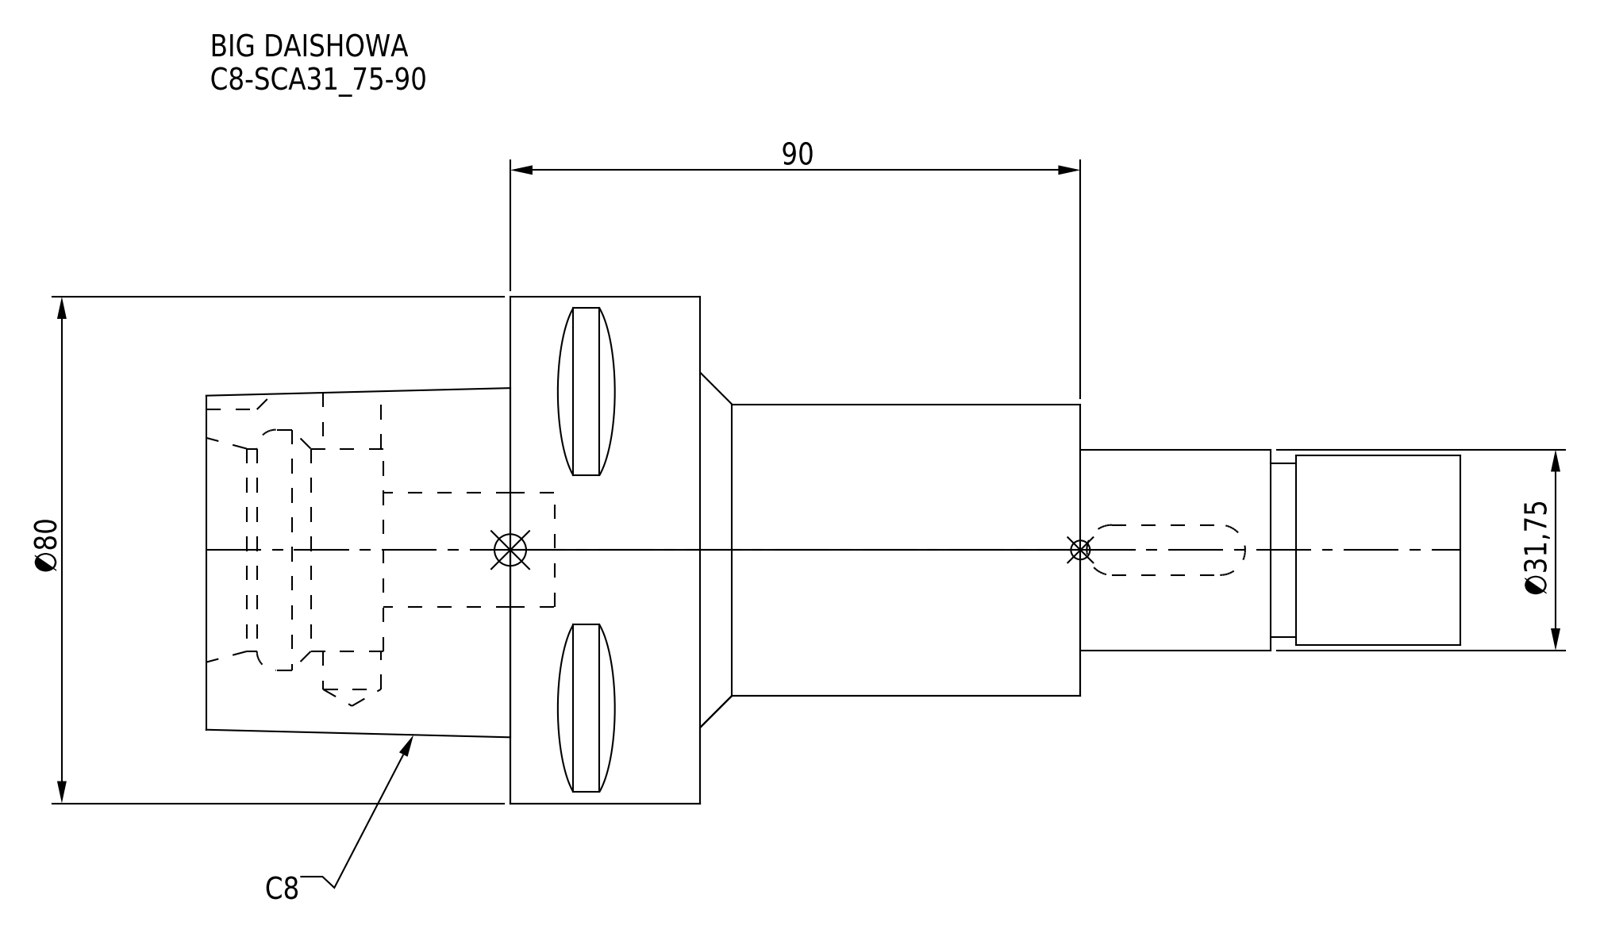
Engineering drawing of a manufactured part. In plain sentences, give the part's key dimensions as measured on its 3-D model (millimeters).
The part is named "C8-SCA31_75-90". Its 3-D file was written by "CREO PARAMETRIC BY PTC INC, 2016380 (AUTOMOTIVE_DESIGN)". It is 1 solid with 71 faces: 34 planar, 25 cylindrical and 12 other. Overall it measures 198 by 80 by 80 millimeters. Its volume is 369 905 cubic millimeters and its surface area 45 529 square millimeters. Round holes: 1 of diameter 9.1, 1 of diameter 18, 1 of diameter 32, 1 of diameter 38. Round bosses or shafts: 1 of diameter 80, 1 of diameter 46, 1 of diameter 31.75, 1 of diameter 30, 1 of diameter 27.5. Partial cylindrical surfaces (rounded edges, fillets, slot ends): 2 of radius 3.96, 1 of radius 6. The main face-to-face distances are 30, 60, 90, 78, 48, 120, 138, 150, 198, 20.
